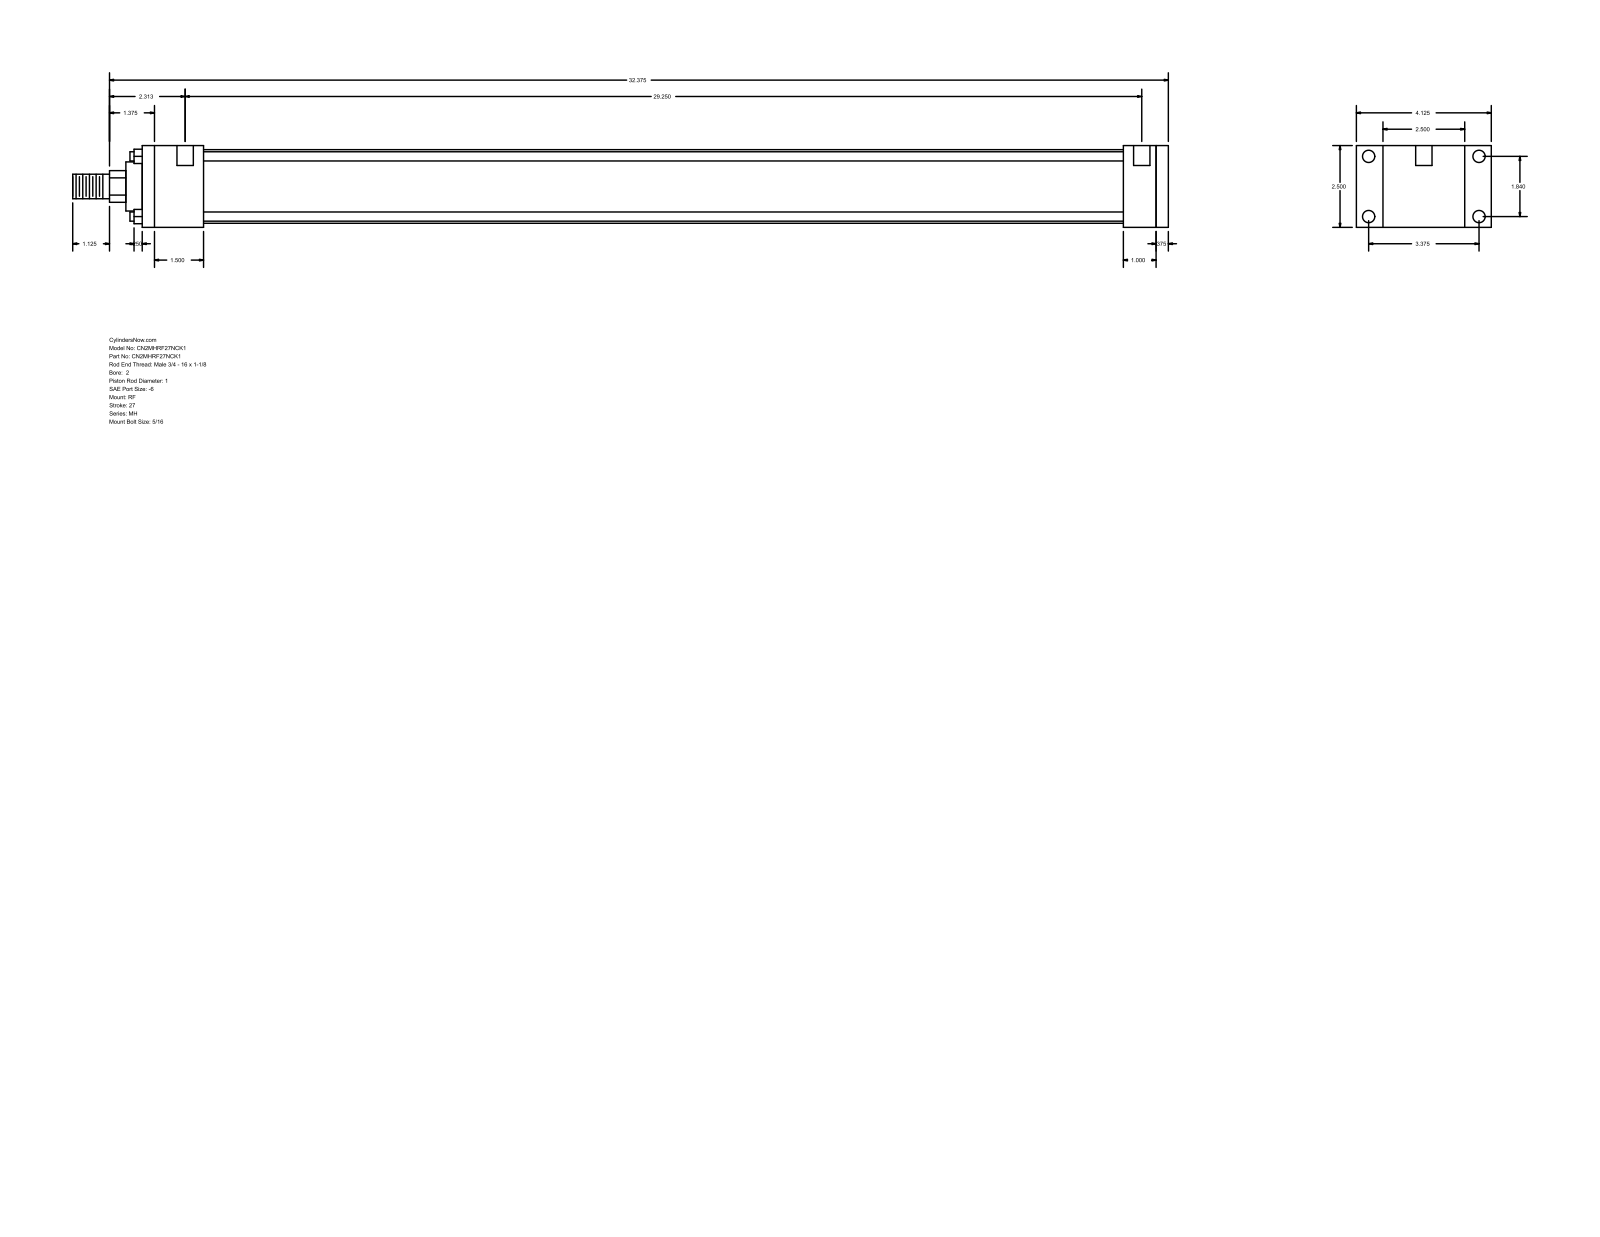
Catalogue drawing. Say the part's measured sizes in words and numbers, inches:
The part is named "MH_RF__0200_1". Its 3-D file was written by "GSSL Pune (CONFIG_CONTROL_DESIGN)". It is 0 solids with 92 faces: 64 planar, 28 cylindrical and 0 other. Overall it measures 33.5 by 4.125 by 2.5 inches. Round holes: 4 of diameter 0.219, 4 of diameter 0.375, 2 of diameter 0.5. Round bosses or shafts: 4 of diameter 0.281, 1 of diameter 2.25, 1 of diameter 1.5, 1 of diameter 1, 1 of diameter 0.75. Partial cylindrical surfaces (rounded edges, fillets, slot ends): 1 of radius 0.484. The main face-to-face distances are 2.5, 31.375, 31, 0.375, 0.813, 1, 1.875, 30, 28.125, 29.125. The hole center spacings are 1.84, 3.375, 3.844, 29.562, 0.125, 0.187, 29.25, 29.375.
